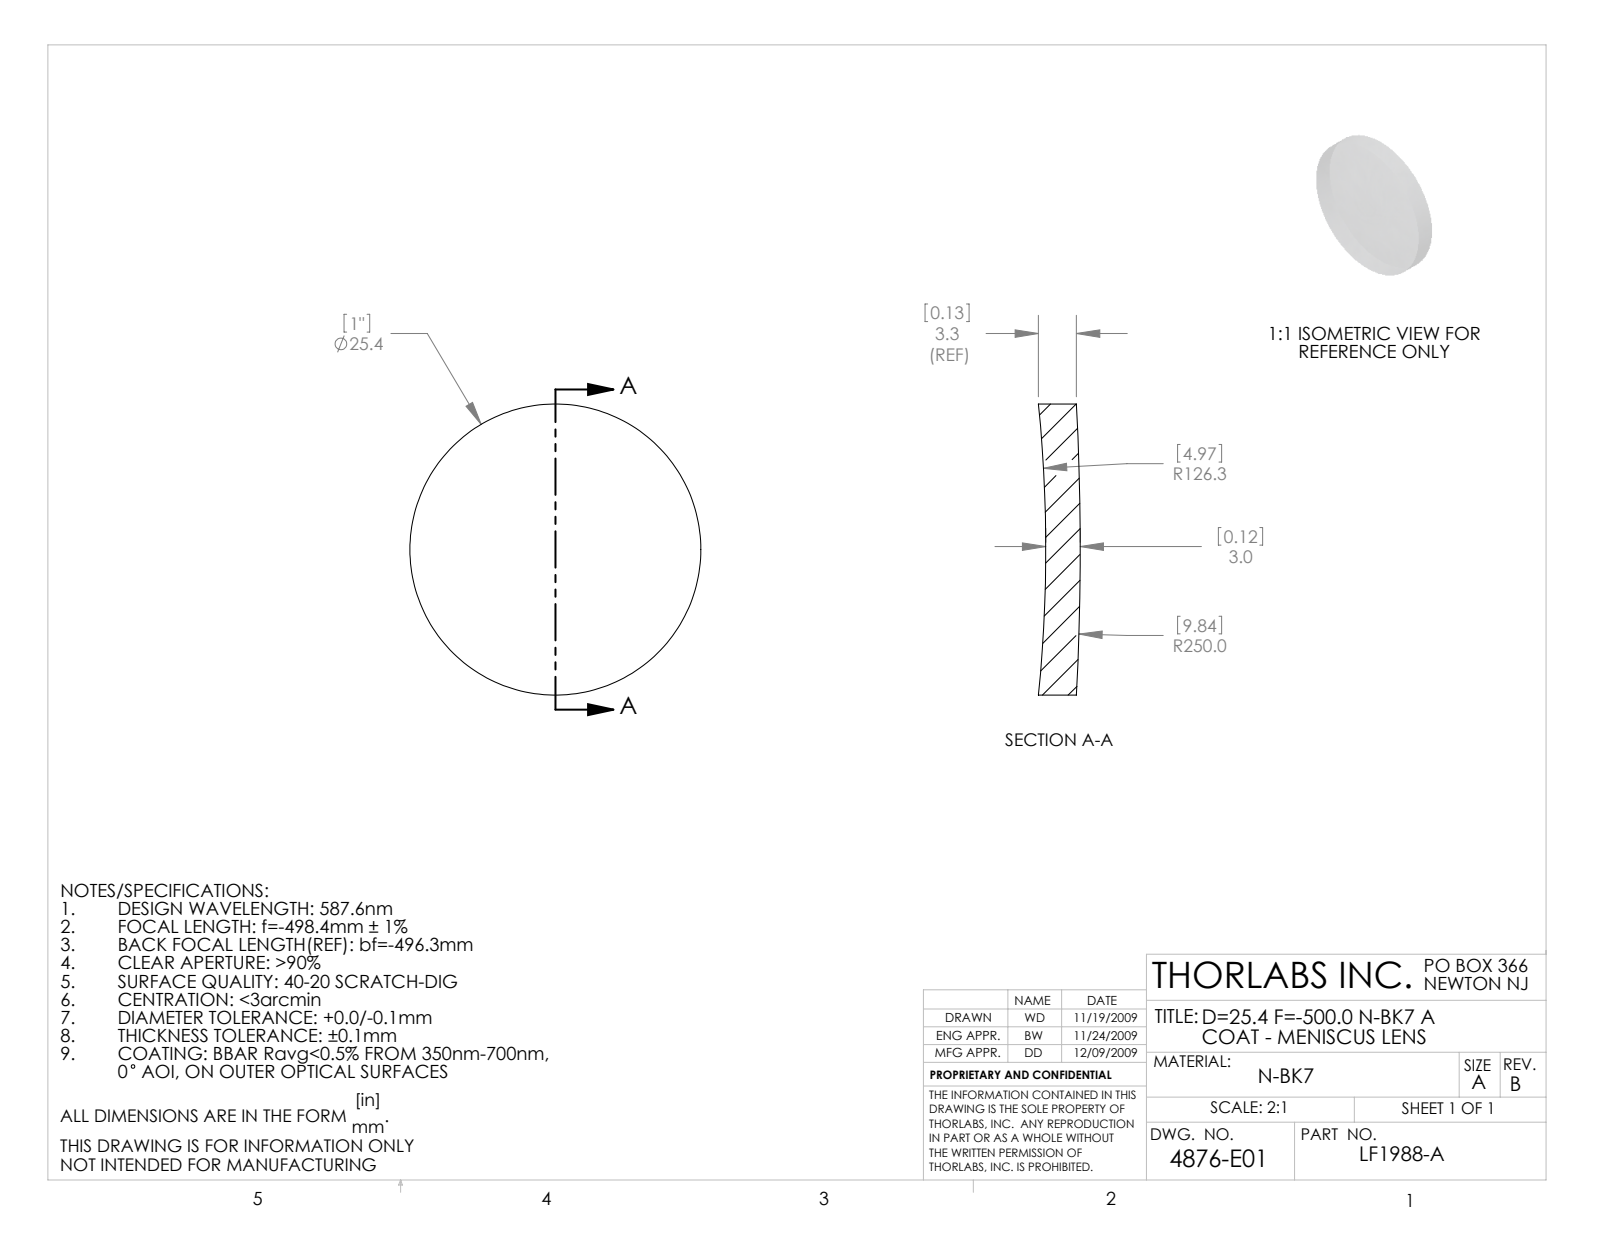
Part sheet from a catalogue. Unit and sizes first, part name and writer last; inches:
Units: inches
Overall size (bounding box): 1 × 1 × 0.143
Round bosses / shafts (diameter × count): ⌀1 ×1
Volume: 0.098 in³ · Surface area: 1.984 in²
Bodies: 1 solid, 6 faces (0 planar, 2 cylindrical, 4 other)
Part name (STEP PRODUCT): 4876-E0W
STEP written by: SolidWorks 2009 (AUTOMOTIVE_DESIGN)
